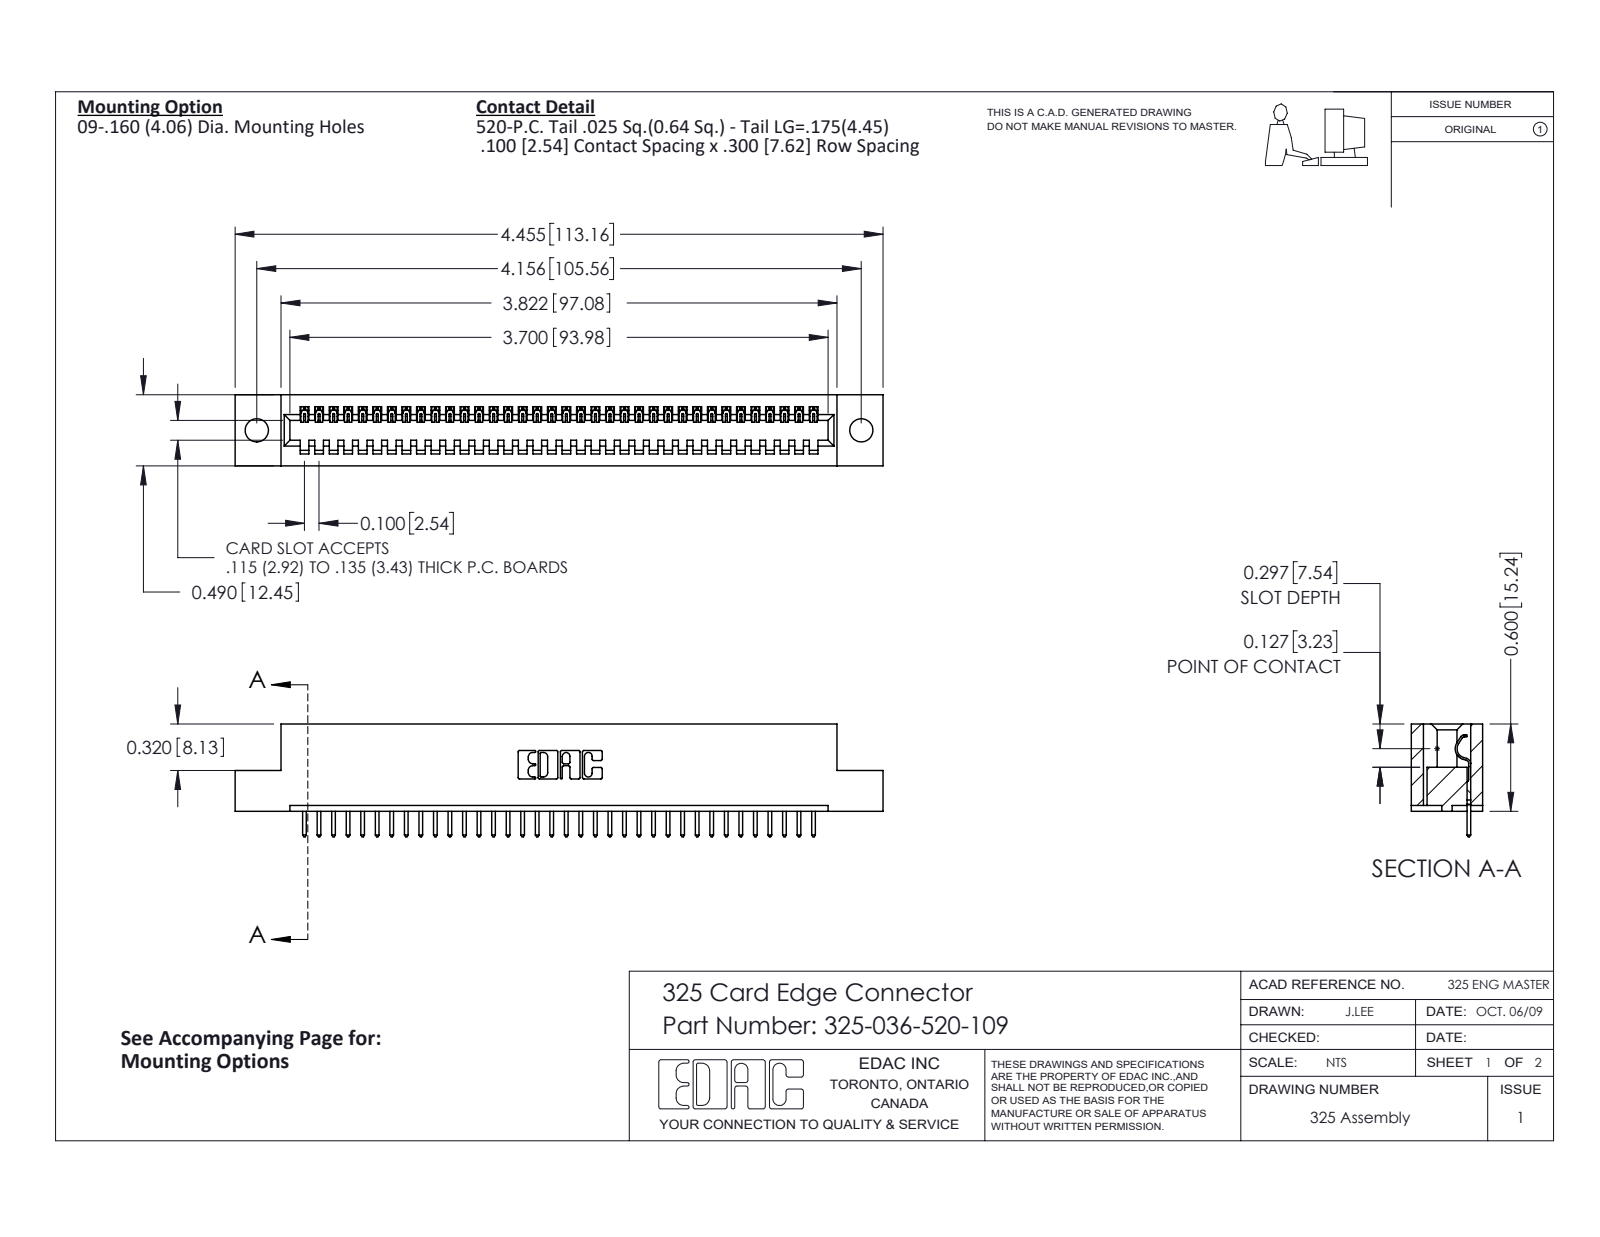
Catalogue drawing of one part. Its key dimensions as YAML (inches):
part_name: "325 Part_.160 TH; 325-292-001_325-293-120; 325-036-520-109"
step_written_by: "SolidWorks 2016 (CONFIG_CONTROL_DESIGN)"
units: inches
bodies: {solids: 37, faces: 2202, planar: 1582, cylindrical: 620, other: 0}
overall_size: [4.455, 0.775, 0.49]
volume: 0.854
surface_area: 22.79
round_holes:
  - {diameter: 0.16, count: 2}
partial_cylinders:
  - {radius: 0.006, count: 72}
  - {radius: 0.01, count: 72}
  - {radius: 0.01, count: 22}
  - {radius: 0.007, count: 6}
  - {radius: 0.031, count: 6}
  - {radius: 0.026, count: 3}
  - {radius: 0.014, count: 1}
  - {radius: 0.022, count: 1}
face_to_face_distances: [0.083, 0.407, 0.49, 0.3, 0.107, 0.383, 0.025, 0.325, 0.56, 0.04]
hole_center_spacings: [4.156]
